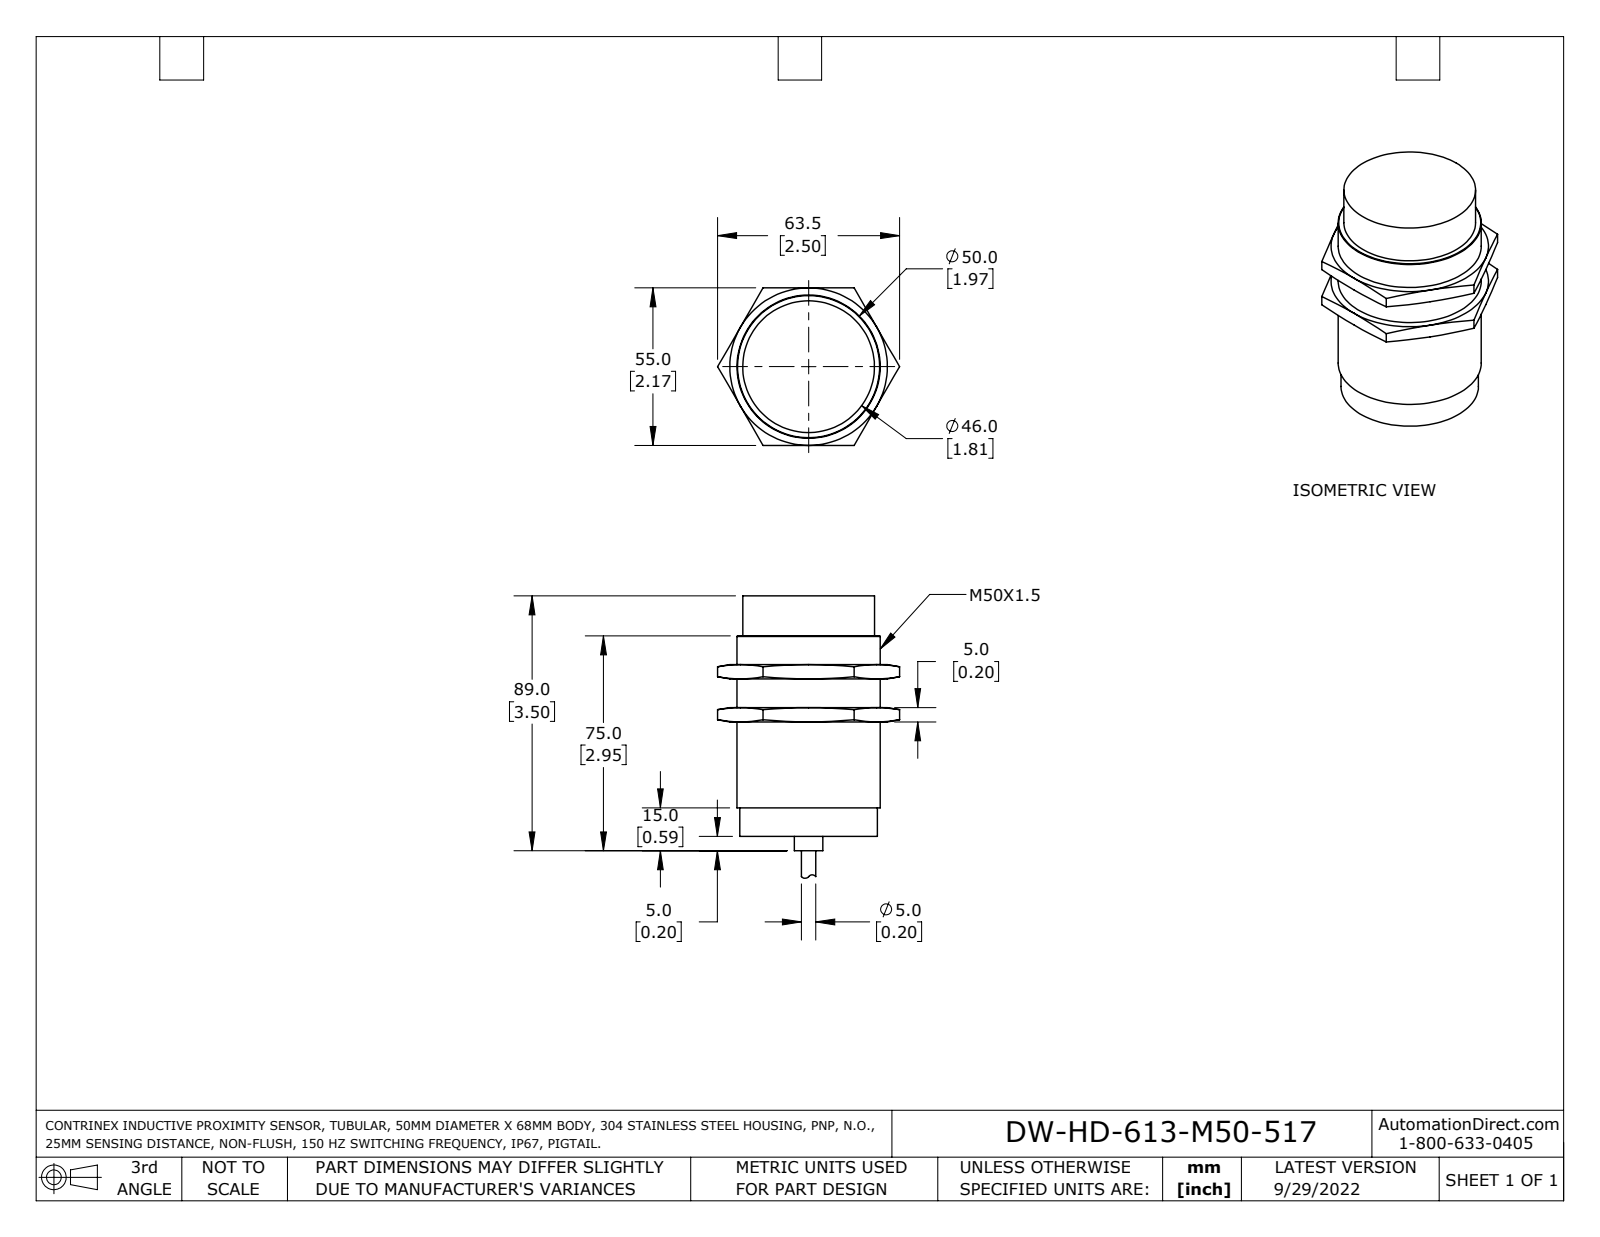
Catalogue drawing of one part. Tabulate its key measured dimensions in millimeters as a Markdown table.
| quantity | value |
| --- | --- |
| part name | DW-HD-613-M50-517 |
| STEP written by | SolidWorks 2021 (AUTOMOTIVE_DESIGN) |
| units | millimeters |
| bodies | 1 solid, 55 faces (21 planar, 9 cylindrical, 25 other) |
| overall size | 98.6 × 63.5 × 55 |
| volume | 166 000 mm³ |
| surface area | 19 940 mm² |
| round bosses / shafts (diameter × count) | 50 × 1, 48 × 1, 46 × 1, 10 × 1, 5 × 1 |
| partial cylindrical surfaces (radius × count) | 1.6 × 2 |
| main face-to-face distances | 84, 55, 15, 5, 10, 60, 45, 30, 24, 39 |
